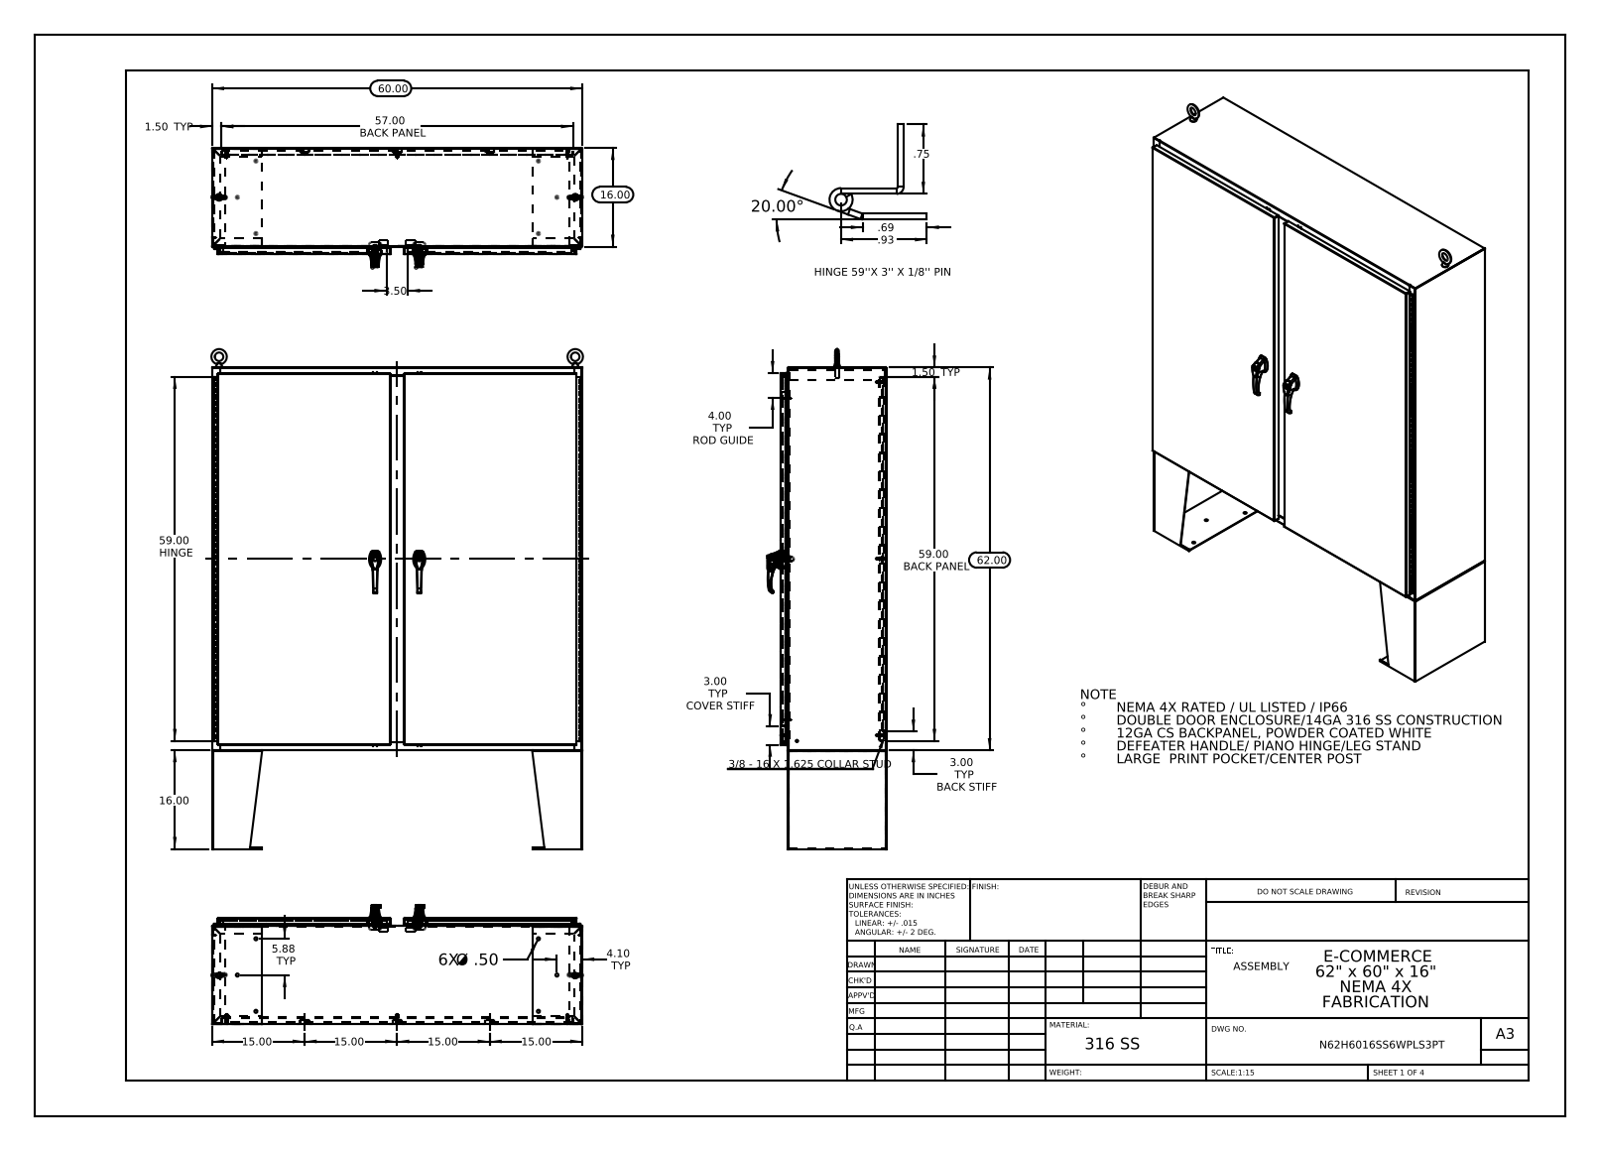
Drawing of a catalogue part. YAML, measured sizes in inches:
part_name: "Quarter-20 CD Stud; N62H6016SSWPLS3PT Backpanel; 10_30 CD Stud; g26103103_26163303 (+8 more)"
step_written_by: "SolidWorks 2013 (CONFIG_CONTROL_DESIGN)"
units: inches
bodies: {solids: 82, faces: 7016, planar: 2786, cylindrical: 2770, other: 1460}
overall_size: [81, 60.226, 19.307]
volume: 1537
surface_area: 37231
round_holes:
  - {diameter: 0.25, count: 20}
  - {diameter: 0.5, count: 14}
  - {diameter: 0.138, count: 6}
  - {diameter: 0.161, count: 6}
  - {diameter: 0.079, count: 4}
  - {diameter: 0.313, count: 4}
  - {diameter: 0.437, count: 4}
  - {diameter: 0.75, count: 4}
  - {diameter: 0.125, count: 2}
  - {diameter: 0.125, count: 2}
  - {diameter: 0.197, count: 2}
  - {diameter: 0.203, count: 2}
round_bosses_or_shafts:
  - {diameter: 0.157, count: 12}
  - {diameter: 0.14, count: 12}
  - {diameter: 0.625, count: 10}
  - {diameter: 0.375, count: 8}
  - {diameter: 0.33, count: 8}
  - {diameter: 0.315, count: 5}
  - {diameter: 0.236, count: 5}
  - {diameter: 1.181, count: 2}
partial_cylinders:
  - {radius: 0.118, count: 72}
  - {radius: 0.006, count: 66}
  - {radius: 0.013, count: 46}
  - {radius: 0.088, count: 38}
  - {radius: 0.039, count: 28}
  - {radius: 0.028, count: 24}
  - {radius: 0.008, count: 12}
  - {radius: 0.02, count: 12}
face_to_face_distances: [0.075, 17.126, 0.104, 17.051, 1.075, 17.201, 1, 16.051, 16.126, 1.179]
hole_center_spacings: [7.152, 24.366, 0.295, 0.625, 0.841, 1.313, 1.561, 7.156]
